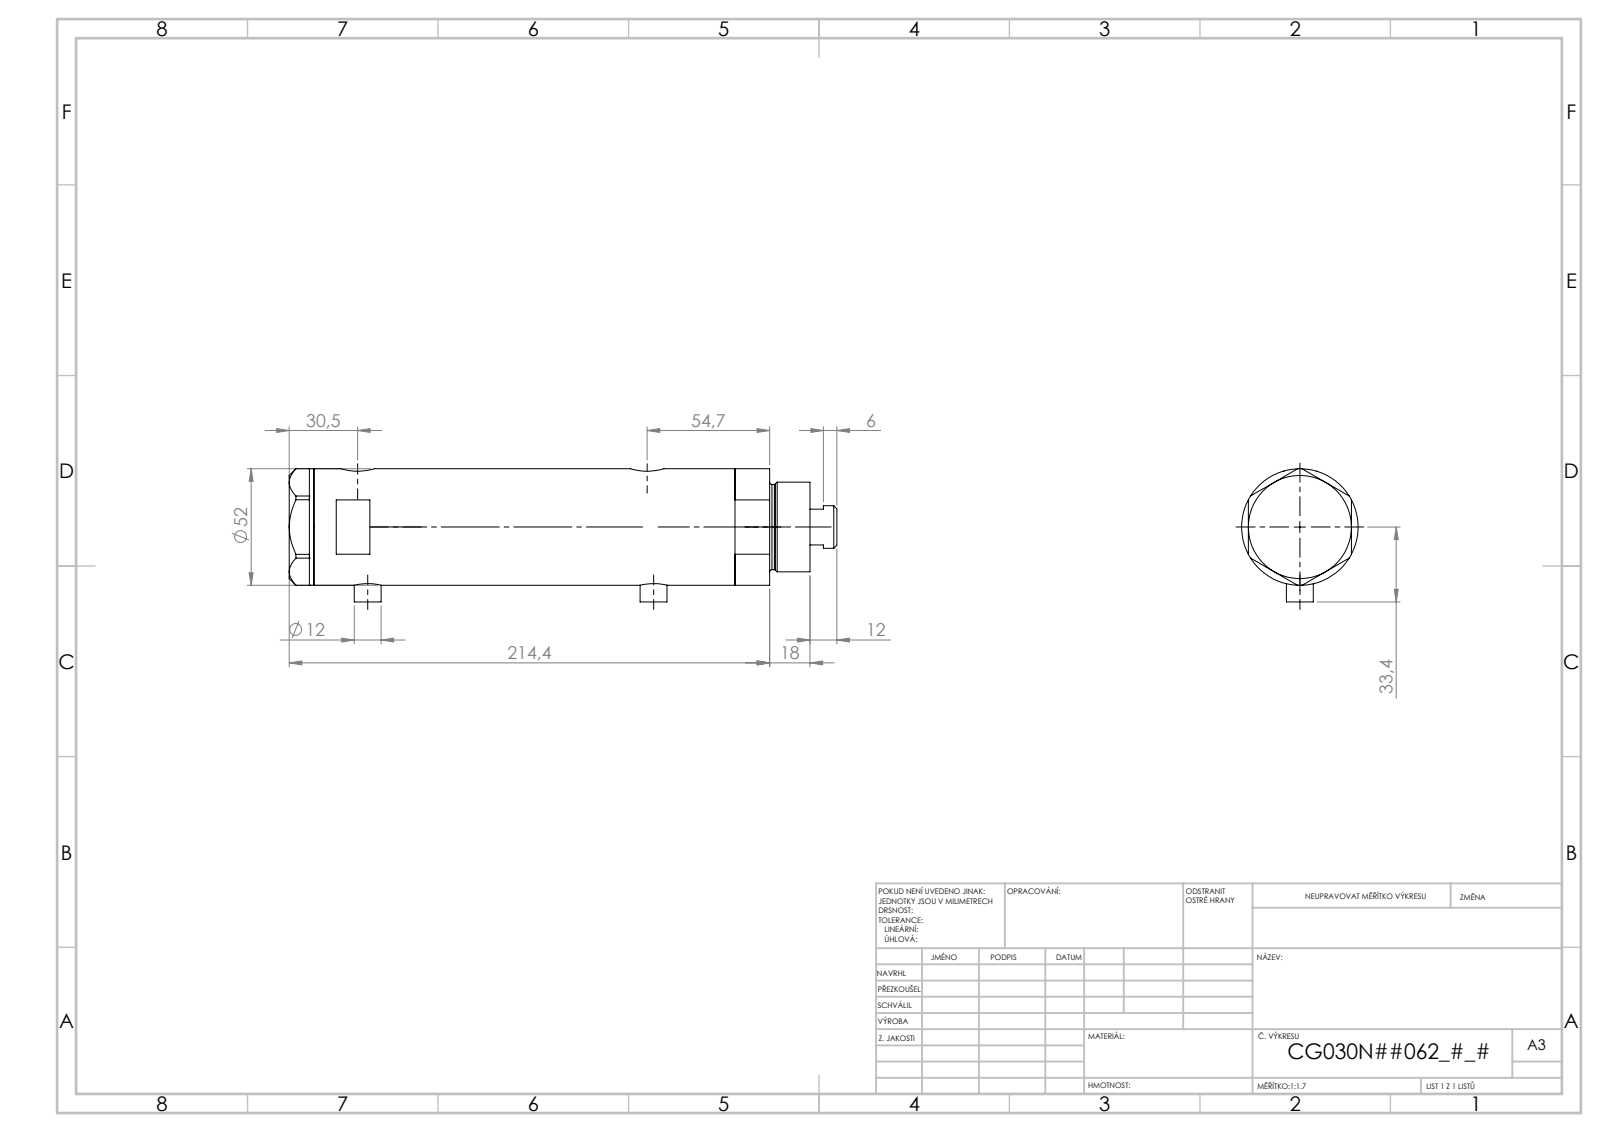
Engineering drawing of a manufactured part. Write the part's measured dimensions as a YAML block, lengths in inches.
part_name: "V270CG_MIDDLE; V270CG_FRONT; V270CG_VC; V270CG_BACK"
step_written_by: "SolidWorks 2019 (CONFIG_CONTROL_DESIGN)"
units: inches
bodies: {solids: 4, faces: 140, planar: 67, cylindrical: 53, other: 20}
overall_size: [8.308, 2.091, 2.047]
volume: 22.87
surface_area: 131.7
round_holes:
  - {diameter: 0.197, count: 2}
  - {diameter: 0.383, count: 2}
  - {diameter: 0.492, count: 2}
  - {diameter: 0.591, count: 2}
  - {diameter: 0.256, count: 1}
  - {diameter: 0.787, count: 1}
  - {diameter: 0.846, count: 1}
  - {diameter: 1.181, count: 1}
  - {diameter: 1.299, count: 1}
  - {diameter: 1.732, count: 1}
round_bosses_or_shafts:
  - {diameter: 0.472, count: 2}
  - {diameter: 2.047, count: 1}
  - {diameter: 1.575, count: 1}
  - {diameter: 1.496, count: 1}
  - {diameter: 0.748, count: 1}
face_to_face_distances: [0.937, 4.982, 1.811, 0.433, 0.433, 4.549, 4.549, 6.415, 5.982, 5.982]
hole_center_spacings: [0.114, 0.177, 3.494, 3.608, 3.671, 3.785, 0.114, 0.115]
